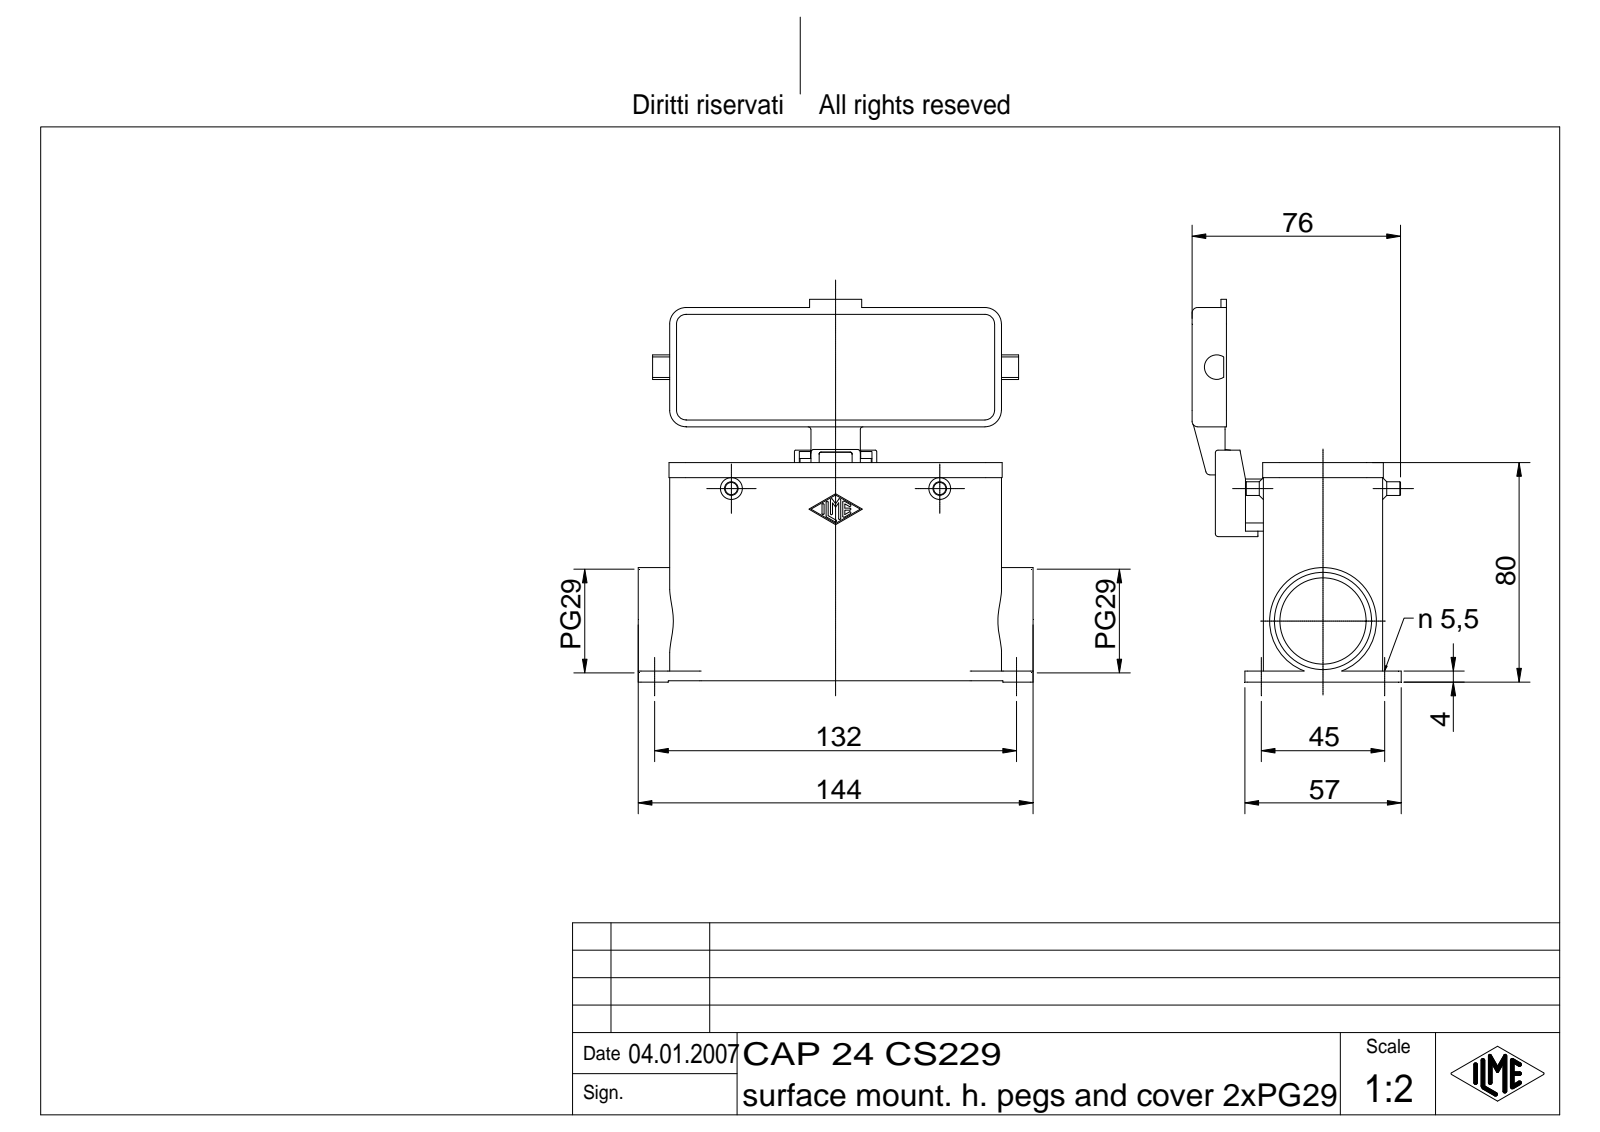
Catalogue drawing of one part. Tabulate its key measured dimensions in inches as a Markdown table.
| quantity | value |
| --- | --- |
| part name | CAP 24 CS229 |
| STEP written by | Autodesk Inventor 7 (AUTOMOTIVE_DESIGN) |
| units | inches |
| bodies | 2 solids, 478 faces (179 planar, 179 cylindrical, 120 other) |
| overall size | 5.669 × 5.492 × 3.002 |
| volume | 9.258 in³ |
| surface area | 138.3 in² |
| round holes (diameter × count) | 0.217 × 4, 0.157 × 1, 0.197 × 1, 1.239 × 1, 1.397 × 1 |
| round bosses / shafts (diameter × count) | 0.197 × 2, 0.118 × 2, 1.535 × 1, 0.276 × 1, 0.157 × 1 |
| partial cylindrical surfaces (radius × count) | 0.039 × 26, 0.015 × 14, 0.236 × 12, 0.02 × 9, 0.028 × 8, 0.079 × 8, 0.118 × 4, 0.138 × 4 |
| main face-to-face distances | 0.118, 1.594, 0.138, 1.713, 1.476, 2.736, 2.618, 0.886, 1.142, 1.024 |
| hole center spacings | 1.772, 5.197, 5.491 |
